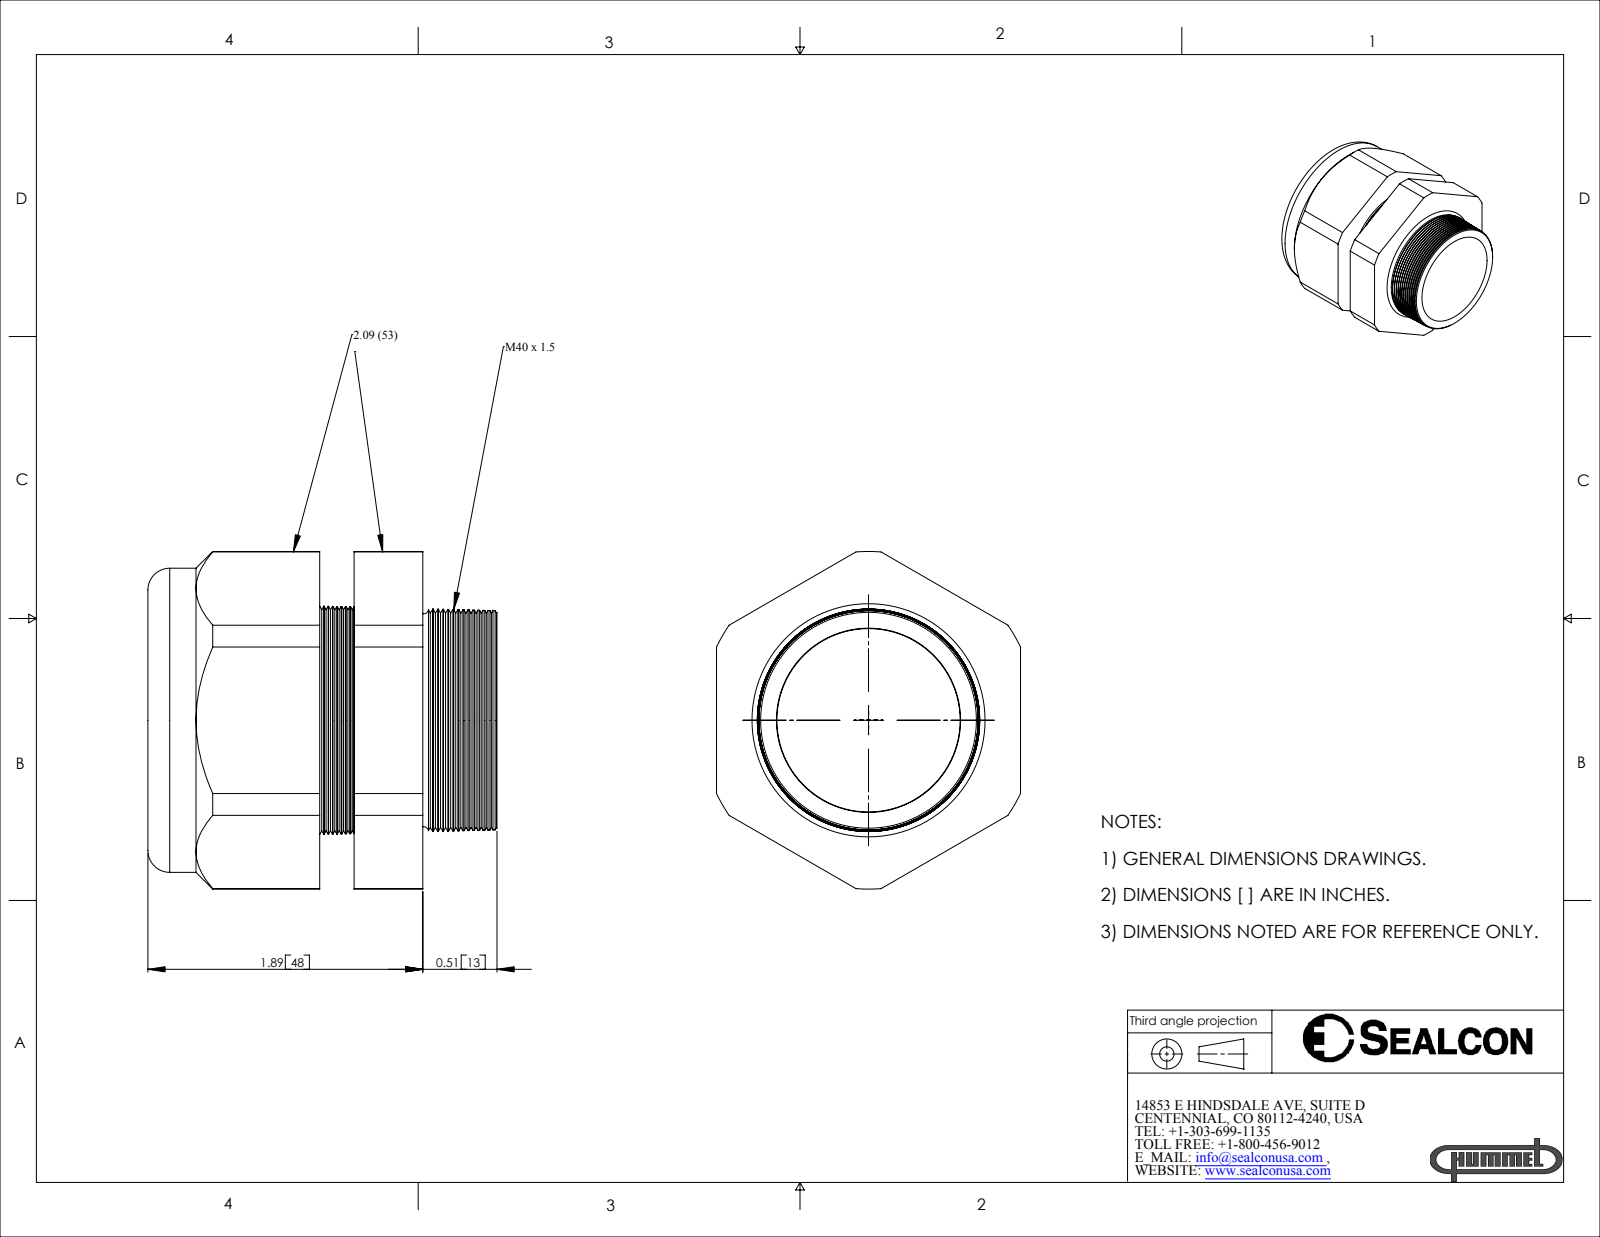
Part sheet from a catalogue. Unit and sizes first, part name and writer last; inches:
Units: inches
Overall size (bounding box): 2.4 × 2.32 × 2.09
Round holes (diameter × count): ⌀1.24 ×1, ⌀1.26 ×1
Round bosses / shafts (diameter × count): ⌀2.09 ×1
Partial cylindrical surfaces — rounded edges, fillets, slot ends (radius × count): R1.16 ×1
Main face-to-face distances: 2.09, 0.237, 0.709, 0.472, 1.181, 1.418, 1.89, 0.5, 0.681, 0.918
Volume: 4.996 in³ · Surface area: 40.16 in²
Bodies: 2 solids, 189 faces (21 planar, 20 cylindrical, 148 other)
Part name (STEP PRODUCT): CD40MP-GY
STEP written by: SolidWorks 2007 (CONFIG_CONTROL_DESIGN)
